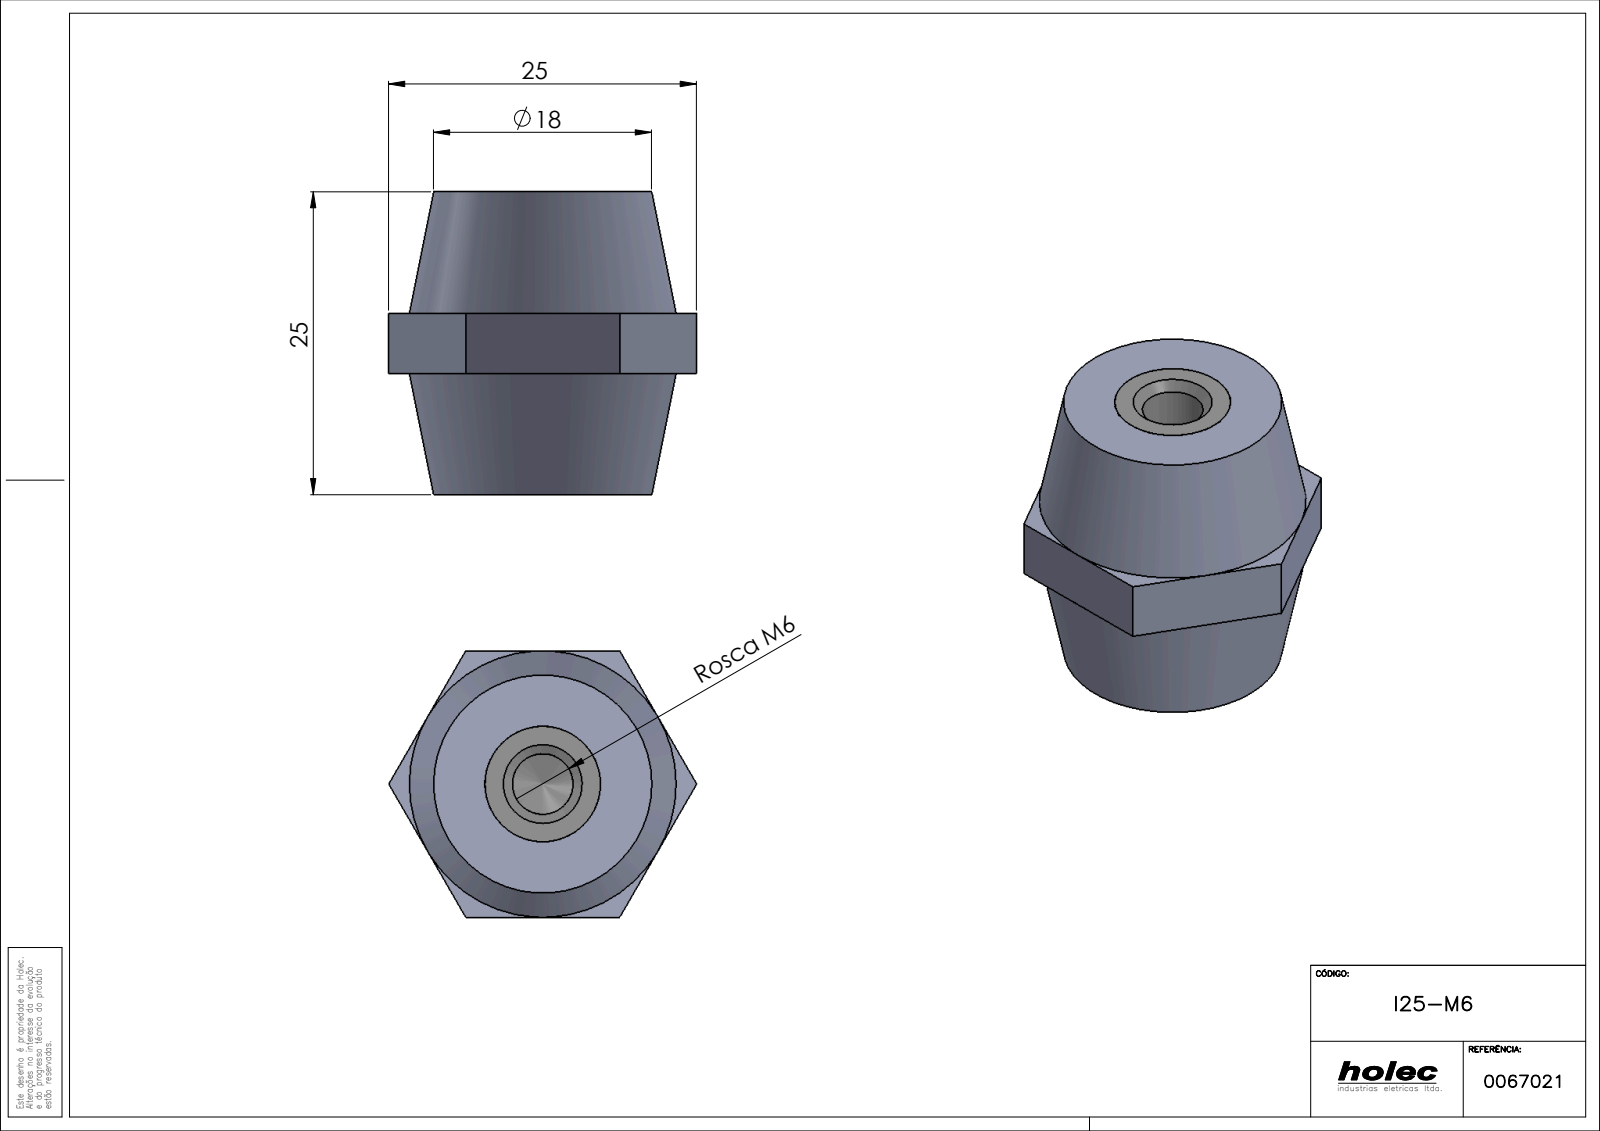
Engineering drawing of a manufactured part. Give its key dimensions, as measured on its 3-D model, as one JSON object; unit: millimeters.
{"part_name": "PB1_0101(PB1_0101_06); I25-M6; PB1_0000", "step_written_by": "SolidWorks 2017 (AUTOMOTIVE_DESIGN)", "units": "millimeters", "bodies": {"solids": 3, "faces": 162, "planar": 82, "cylindrical": 12, "other": 68}, "overall_size": [25.4, 25, 22], "volume_mm3": 8136, "surface_area_mm2": 3920, "round_holes": [[5, 1], [8, 1]], "face_to_face_distances": [9.52, 17.01, 25, 17, 22, 2.5, 5.5, 7.99, 8, 9.01]}
